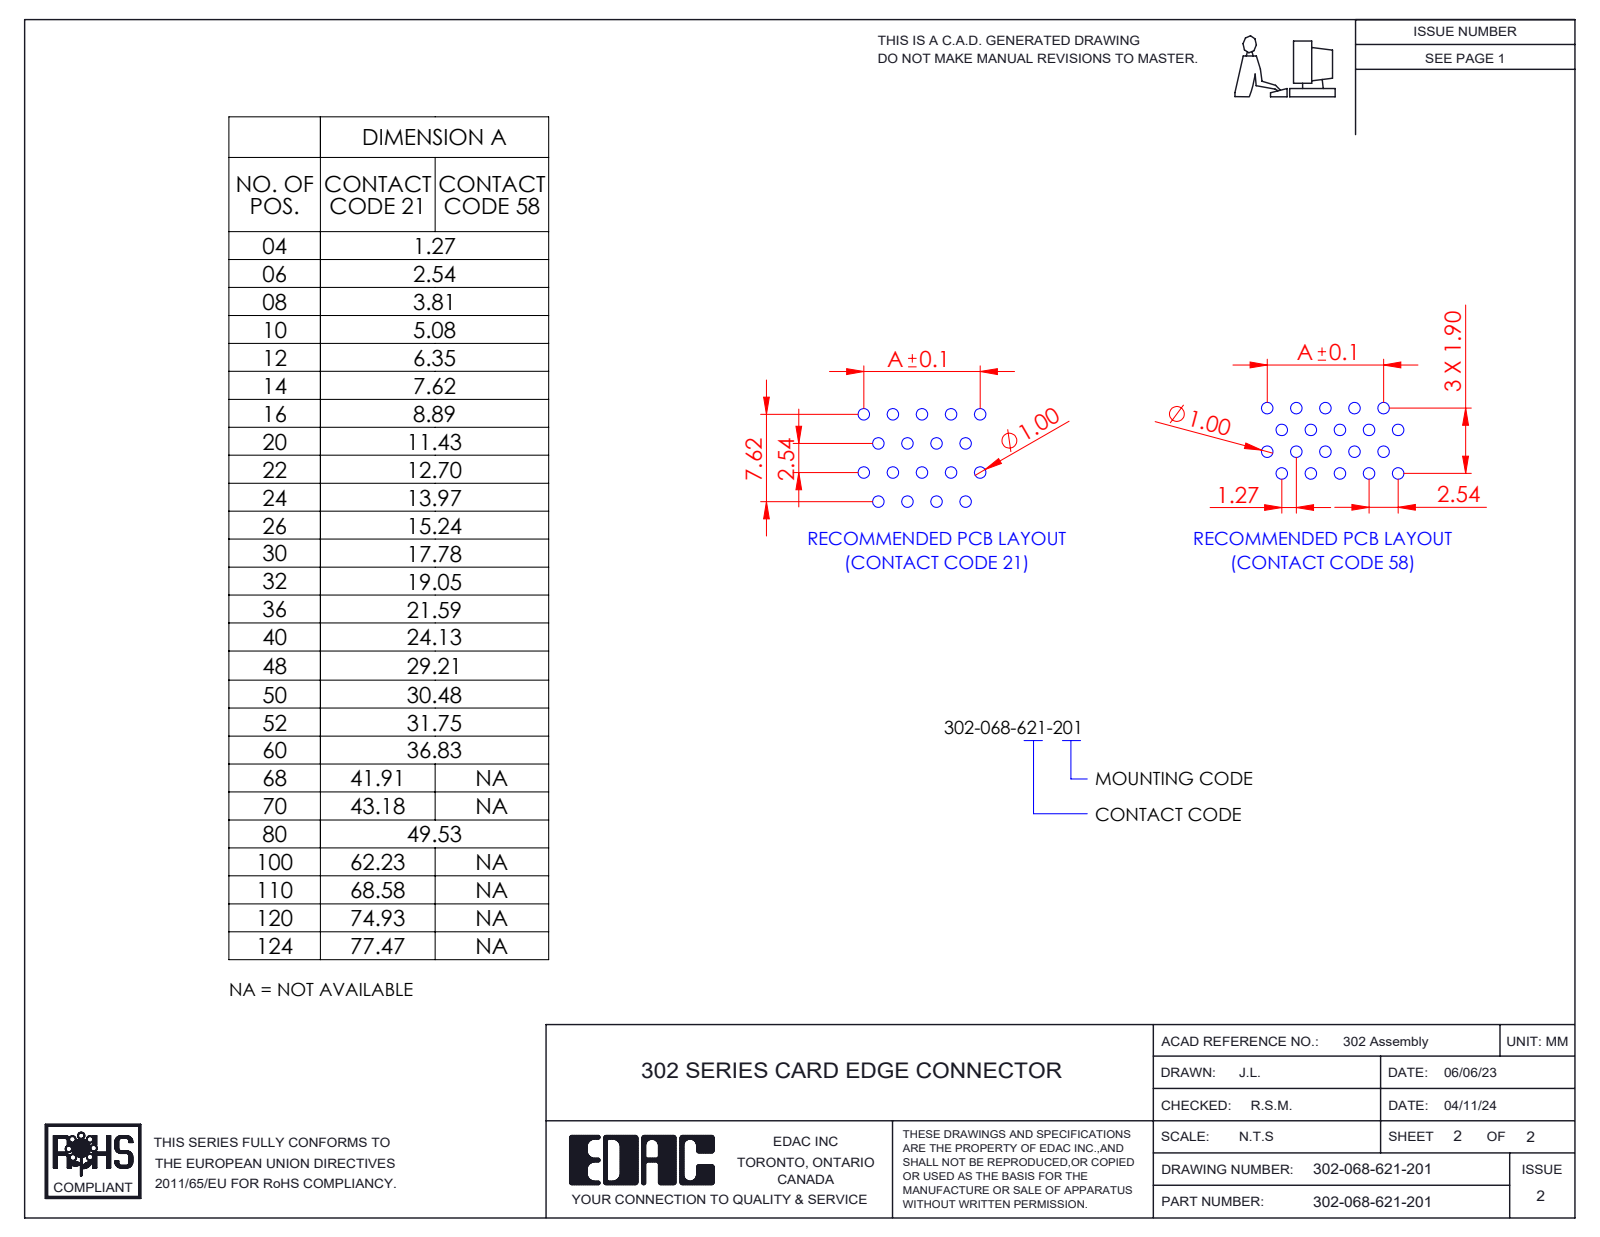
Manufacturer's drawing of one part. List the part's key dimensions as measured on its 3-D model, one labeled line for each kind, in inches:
Part name (STEP PRODUCT): Contact_302-290-X21 (1); 302-068-621-201; HSG_Vertical HSG; Contact_302-290-X21 (2)
STEP written by: SolidWorks 2023 (CONFIG_CONTROL_DESIGN)
Units: inches
Bodies: 69 solids, 3160 faces (2327 planar, 693 cylindrical, 140 other)
Overall size (bounding box): 1.94 × 0.694 × 0.35
Volume: 0.234 in³ · Surface area: 16.21 in²
Partial cylindrical surfaces — rounded edges, fillets, slot ends (radius × count): R0.008 ×76, R0.08 ×4, R0.082 ×4, R0.004 ×2, R0.016 ×2, R0.016 ×2, R0.049 ×2, R0.06 ×2
Main face-to-face distances: 0.1, 0.05, 0.2, 0.15, 0.3, 0.25, 0.35, 0.35, 0.4, 0.45
